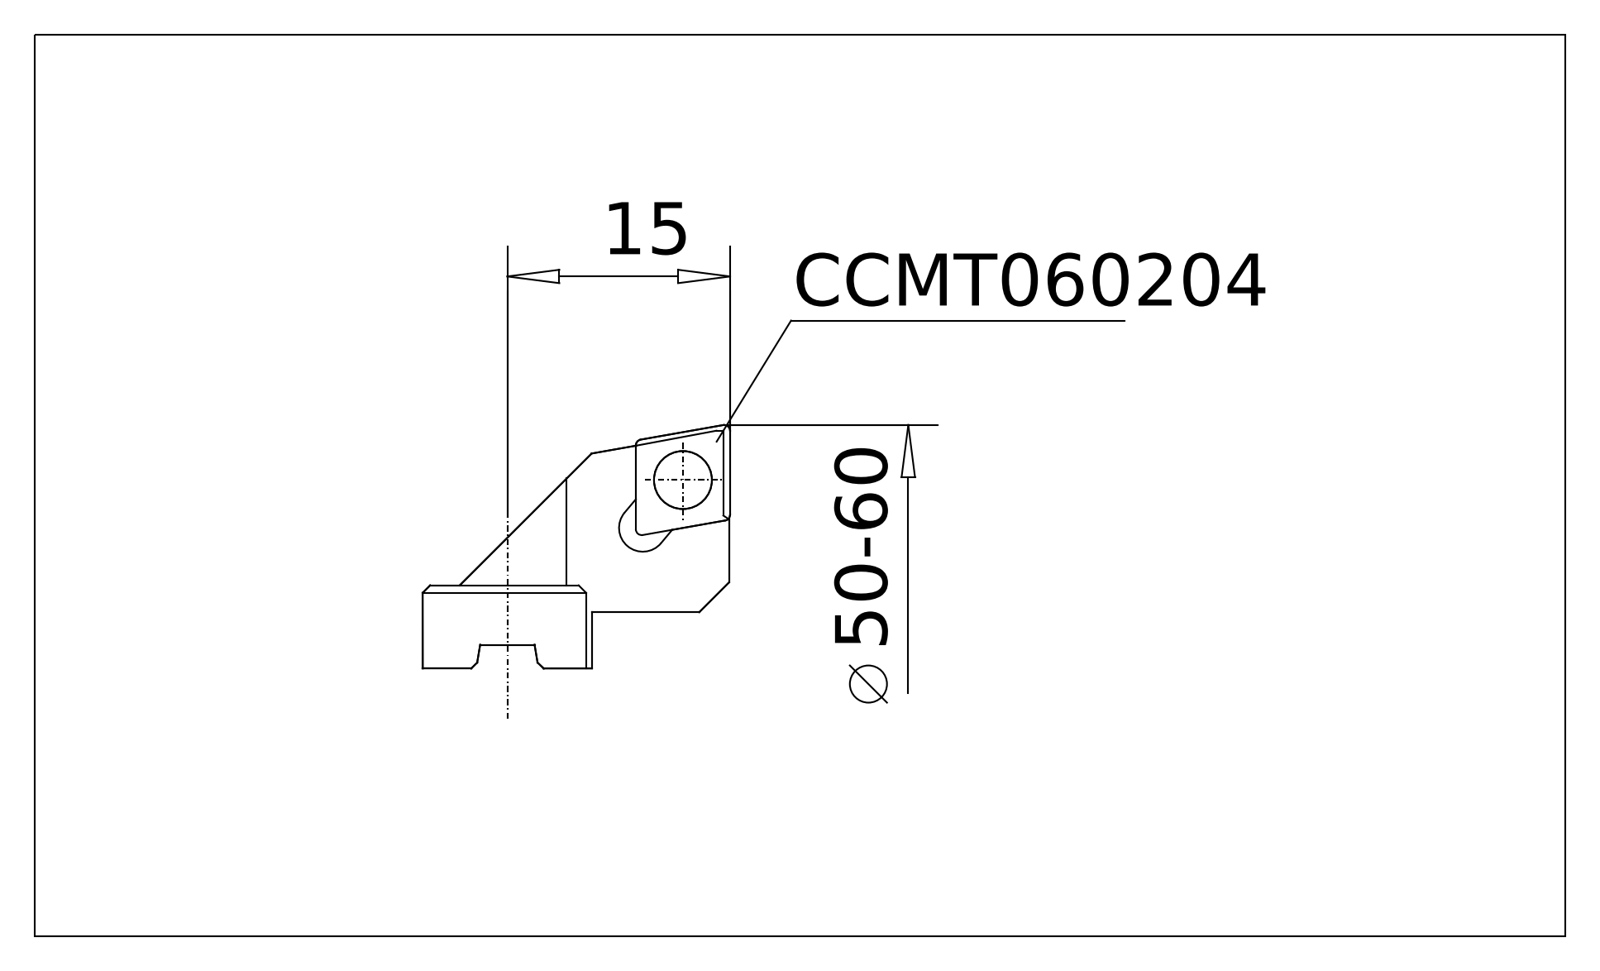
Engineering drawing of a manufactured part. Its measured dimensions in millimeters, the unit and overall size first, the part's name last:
Units: millimetres
Overall size (bounding box): 20.7 × 16.4 × 11.92
Round holes (diameter × count): ⌀2 ×1, ⌀2.8 ×1, ⌀4 ×1, ⌀8 ×1
Round bosses / shafts (diameter × count): ⌀3.45 ×1, ⌀2.5 ×1
Partial cylindrical surfaces — rounded edges, fillets, slot ends (radius × count): R0.15 ×6, R0.4 ×6, R1.6 ×1, R5.7 ×1
Main face-to-face distances: 5.6, 2.1, 3.5, 3.8, 2.2, 1.6, 0.9, 1.3, 2.9, 2.38
Volume: 1 048 mm³ · Surface area: 1 159 mm²
Bodies: 3 solids, 109 faces (39 planar, 34 cylindrical, 36 other)
Part name (STEP PRODUCT): 626.333 Kaiser ENH 33 CC06 50-60|654.852 Kaiser CCMT 060204 K20C_Standard;NONE; 626.333 Kaiser ENH 33 CC06 50-60|694.122 Kaiser ETL M2.5x6.5 T7 IP 10S_Standard;NONE; 626.333 Kaiser ENH 33 CC06 50-60|626.333 Kaiser ENH 33 CC06 50-60_Standard;NONE
STEP written by: ACIS (automotive_design)
